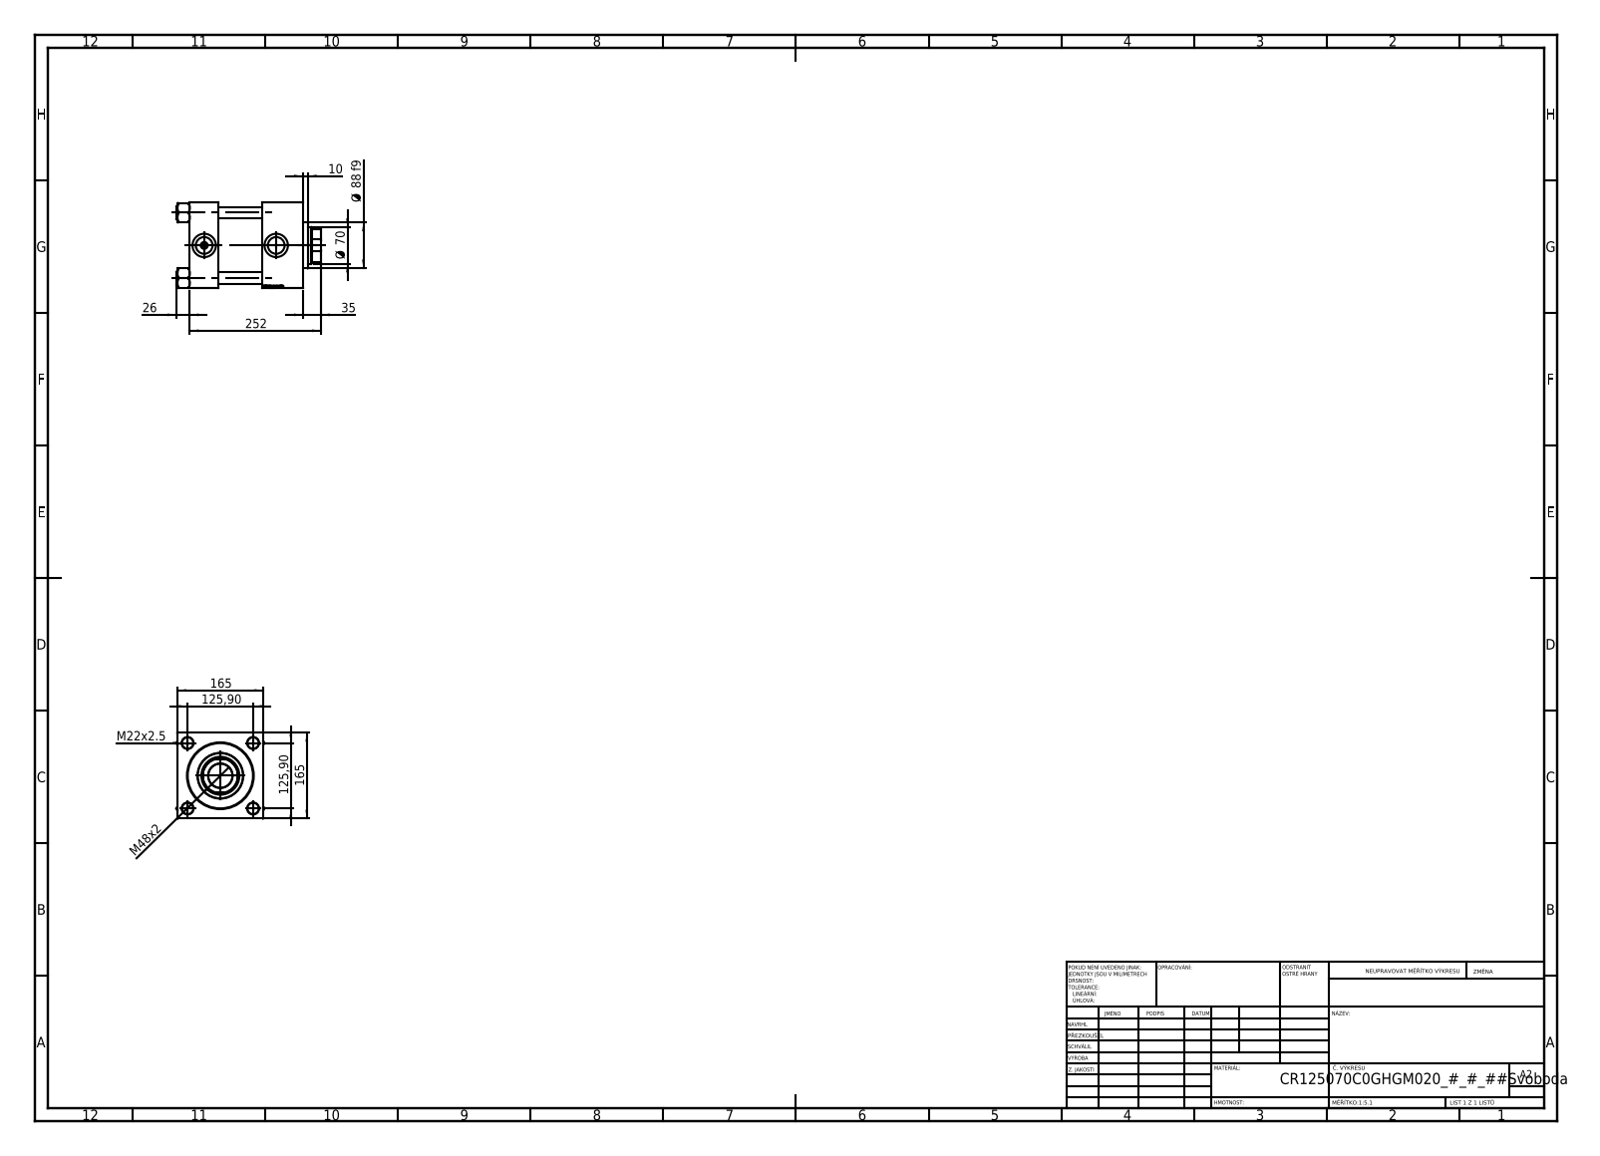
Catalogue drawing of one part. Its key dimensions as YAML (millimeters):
part_name: "V215CR_C_Body; V215_VC_A; V215CR_C_TYCINKA; NUT_M5_C (+1 more)"
step_written_by: "SolidWorks 2019 (CONFIG_CONTROL_DESIGN)"
units: millimeters
bodies: {solids: 11, faces: 1196, planar: 574, cylindrical: 86, other: 536}
overall_size: [278, 169.14, 165]
volume: 4603000
surface_area: 511214
round_holes:
  - {diameter: 22, count: 4}
  - {diameter: 7, count: 2}
  - {diameter: 32.24, count: 2}
  - {diameter: 45, count: 2}
  - {diameter: 46.5, count: 1}
  - {diameter: 70, count: 1}
  - {diameter: 73, count: 1}
  - {diameter: 96, count: 1}
  - {diameter: 125, count: 1}
  - {diameter: 125.5, count: 1}
round_bosses_or_shafts:
  - {diameter: 25, count: 4}
  - {diameter: 131, count: 1}
  - {diameter: 88, count: 1}
partial_cylinders:
  - {radius: 34, count: 1}
face_to_face_distances: [165, 55, 162, 217, 139, 84, 78, 188.3, 133.3, 49.3]
hole_center_spacings: [89.02, 125.9, 178.05, 138.5]
